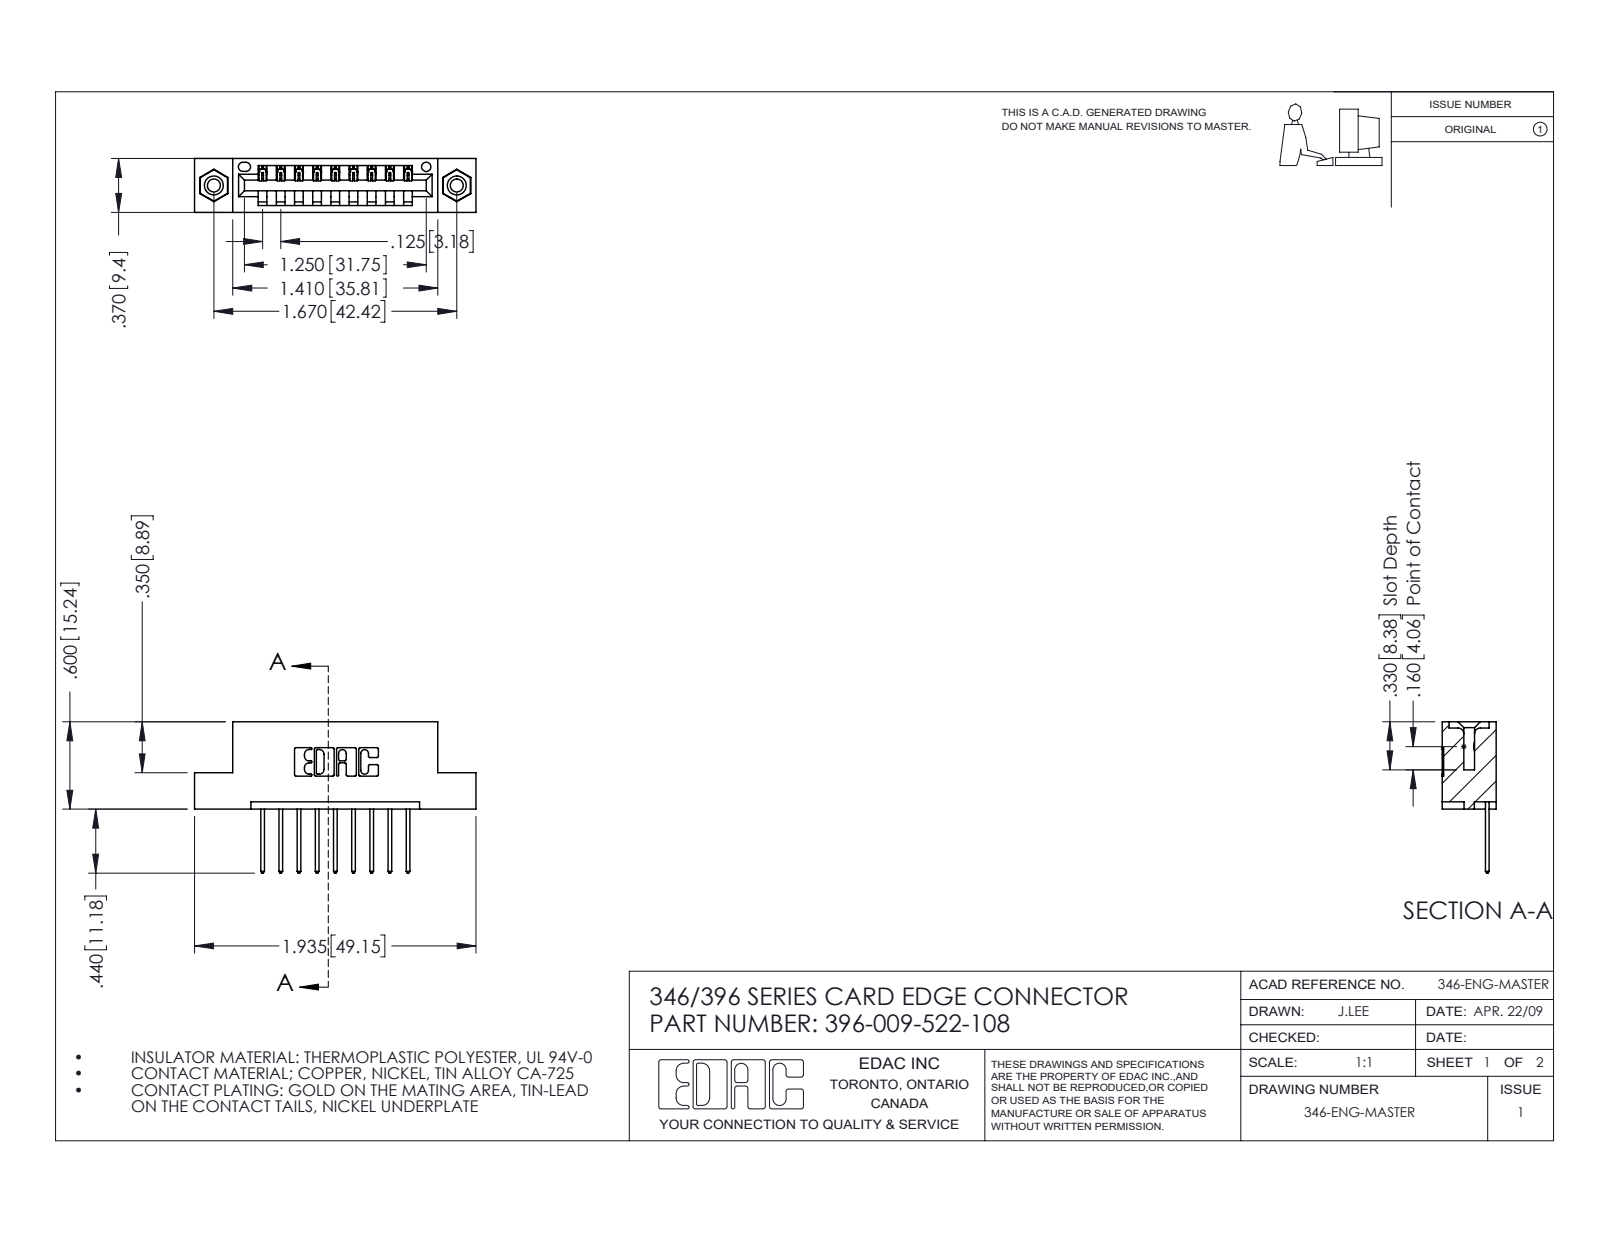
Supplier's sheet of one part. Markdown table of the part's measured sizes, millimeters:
| quantity | value |
| --- | --- |
| part name | 346 Part_Flush Mounting Lugs - 0.156 Dia-TI; 396-009-522-108; 345-250-001_345-250-003-102; 345-292-001_345-293-122 |
| STEP written by | SolidWorks 2016 (CONFIG_CONTROL_DESIGN) |
| units | millimeters |
| bodies | 12 solids, 704 faces (468 planar, 220 cylindrical, 16 other) |
| overall size | 49.1 × 26.4 × 9.4 |
| volume | 4 470 mm³ |
| surface area | 5 288 mm² |
| round holes (diameter × count) | 2.3 × 2, 3.2 × 2, 4 × 2, 1.6 × 1 |
| round bosses / shafts (diameter × count) | 3.9 × 2 |
| partial cylindrical surfaces (radius × count) | 0.3 × 22, 0.2 × 18, 0.3 × 18, 0.2 × 6, 0.8 × 6, 0.7 × 3, 0.8 × 2, 1 × 2 |
| main face-to-face distances | 6.4, 1.2, 8.2, 9.4, 1.8, 7.6, 0.6, 3.8, 5.6, 2.5 |
| hole center spacings | 6.2, 37.2, 42.4 |
